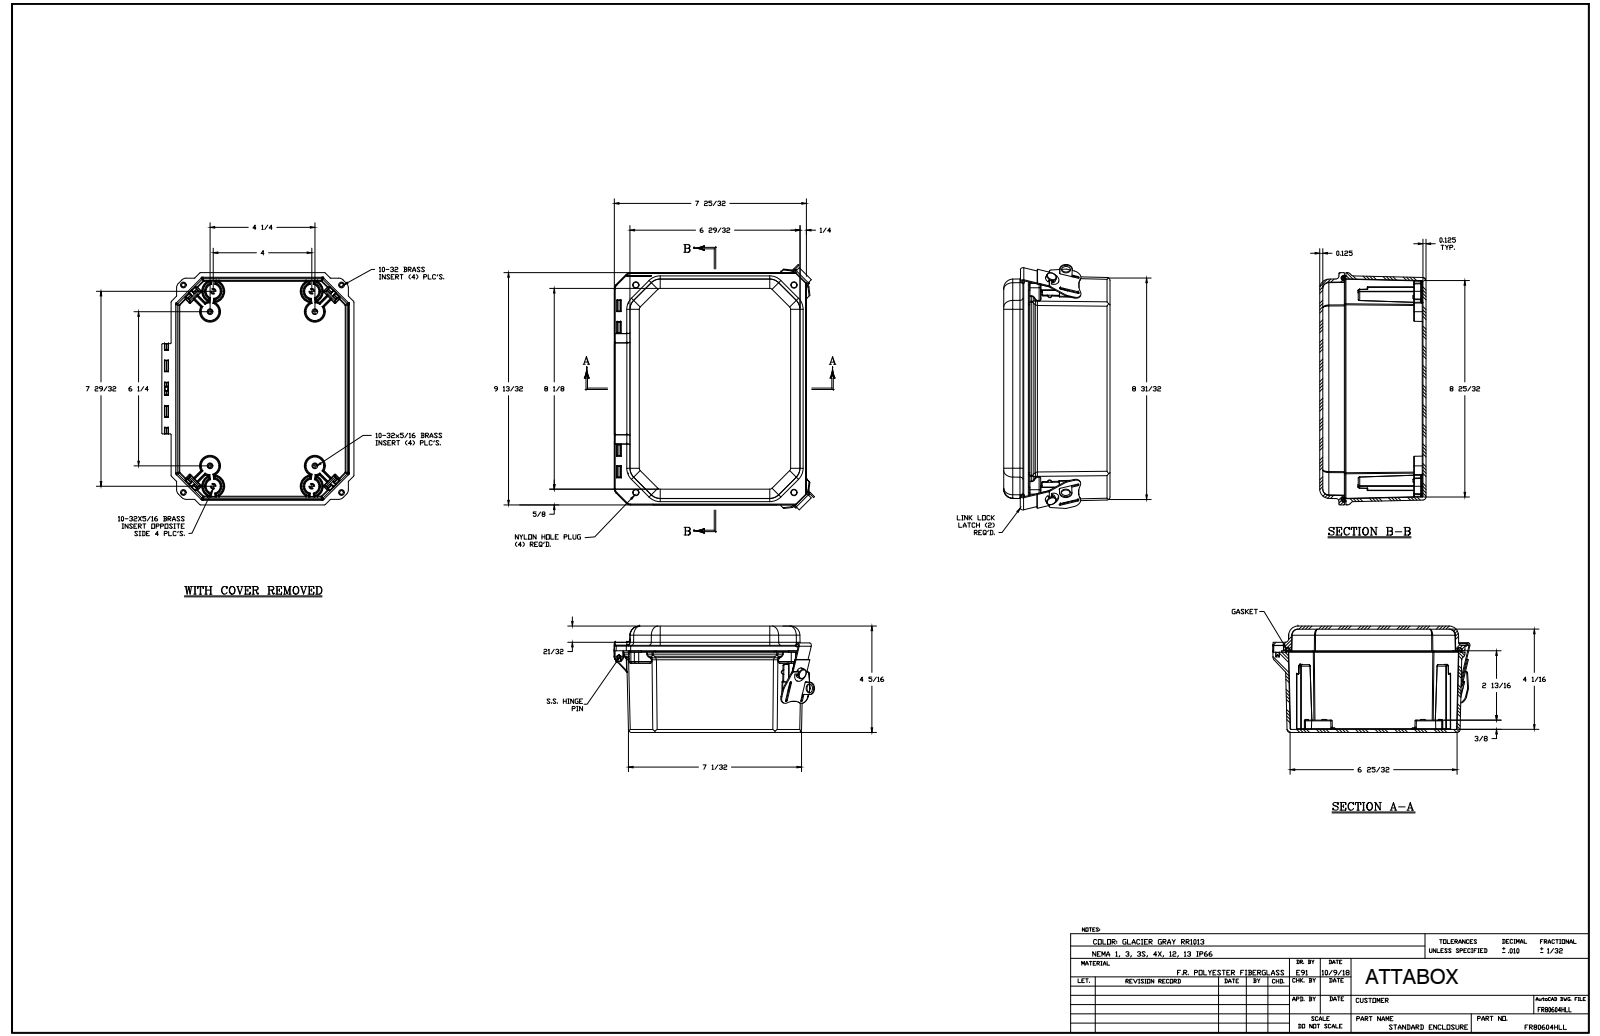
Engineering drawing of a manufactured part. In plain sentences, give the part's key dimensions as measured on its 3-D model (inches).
The part is named "FR80604HLL". Its 3-D file was written by "SolidWorks 2018 (AUTOMOTIVE_DESIGN)". It is 37 solids with 2200 faces: 757 planar, 855 cylindrical and 588 other. Overall it measures 10.242 by 8.241 by 4.31 inches. Its volume is 45.1 cubic inches and its surface area 634.5 square inches. Round holes: 16 of diameter 0.156, 8 of diameter 0.152, 4 of diameter 0.15, 4 of diameter 0.252, 4 of diameter 0.253, 3 of diameter 0.098, 2 of diameter 0.05, 2 of diameter 0.12, 2 of diameter 0.219, 2 of diameter 0.227, 2 of diameter 0.313, 2 of diameter 0.363. Round bosses or shafts: 16 of diameter 0.246, 4 of diameter 0.87, 4 of diameter 0.209, 3 of diameter 0.2, 3 of diameter 0.135, 3 of diameter 0.05, 2 of diameter 0.6, 2 of diameter 0.435. Partial cylindrical surfaces (rounded edges, fillets, slot ends): 124 of radius 0.01, 80 of radius 0.005, 65 of radius 0.02, 43 of radius 0.03, 34 of radius 0.125, 28 of radius 0.039, 24 of radius 0.03, 24 of radius 0.09. The main face-to-face distances are 0.125, 4.185, 4.31, 4.061, 0.25, 0.124, 3.935, 0.125, 4.06, 0.375. The hole center spacings are 1.531, 8.193, 9.065, 9.067, 0.837, 7.08, 7.411, 7.412.
